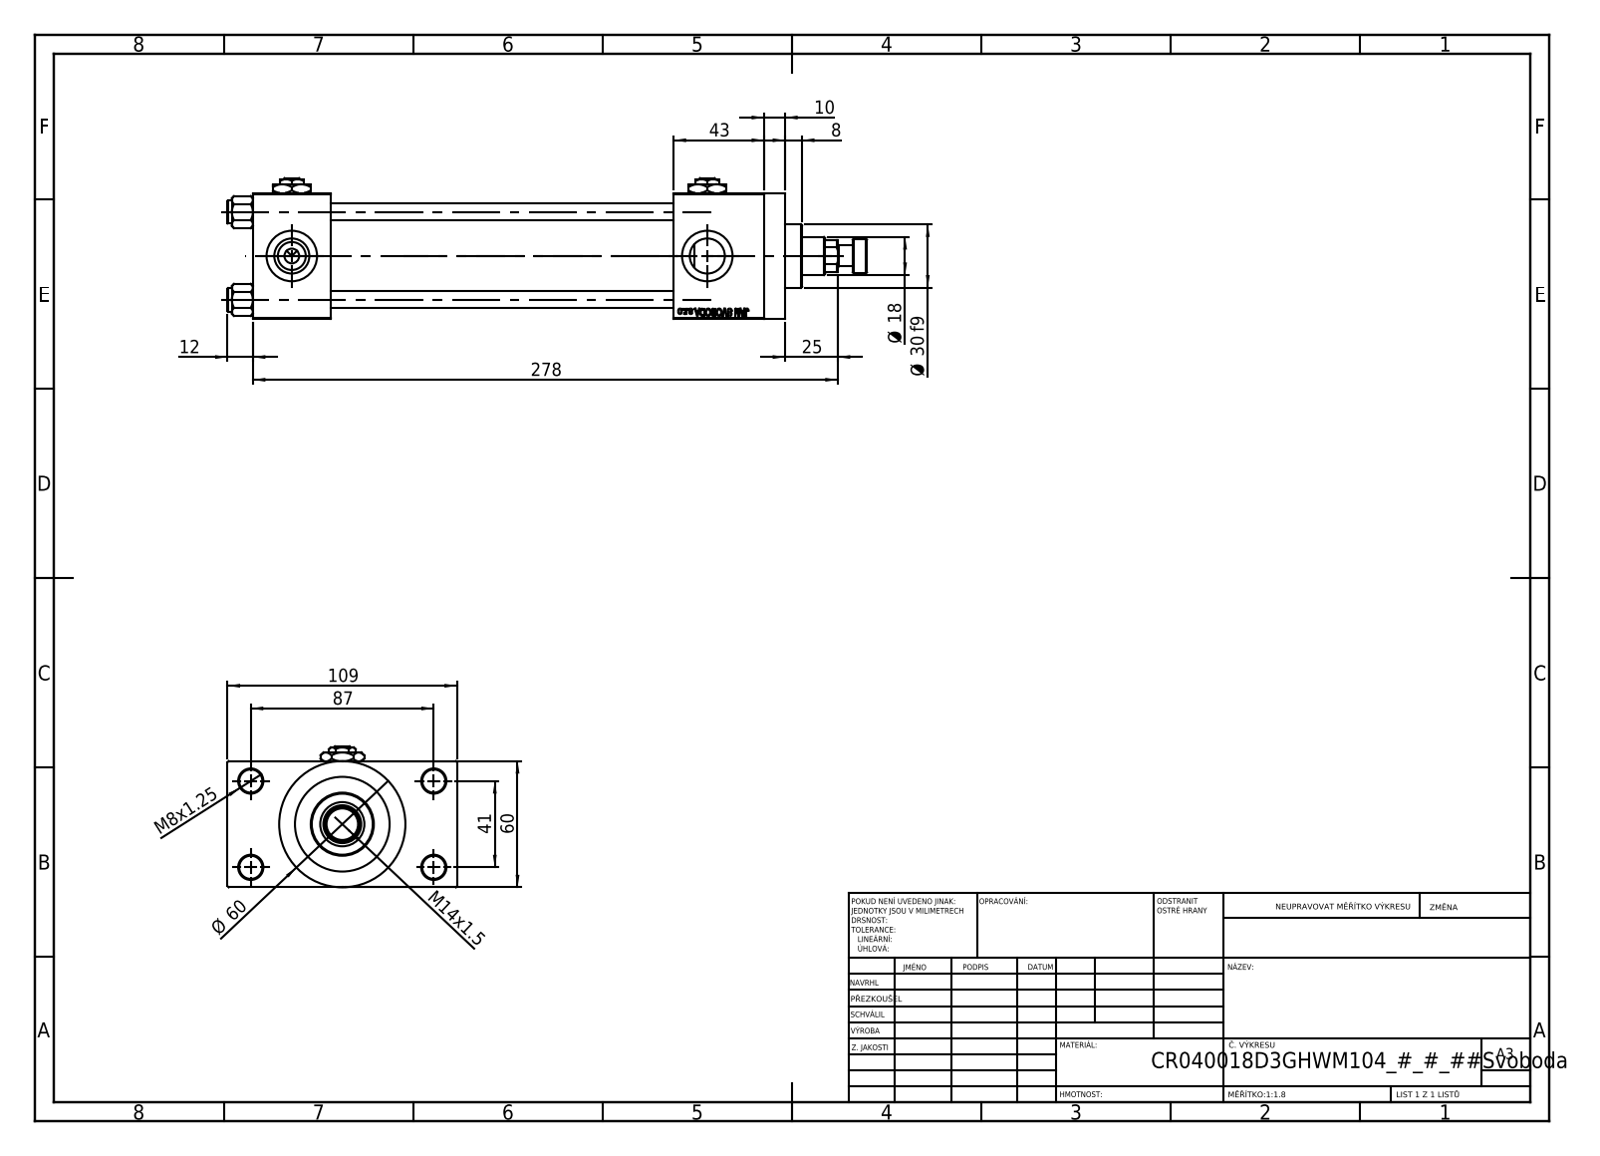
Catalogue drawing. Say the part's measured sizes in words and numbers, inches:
The part is named "V215_VC_A; V215CR_ROD_END_W; NUT_M5_D; V215CR_D_Body (+3 more)". Its 3-D file was written by "SolidWorks 2019 (CONFIG_CONTROL_DESIGN)". It is 14 solids with 1218 faces: 549 planar, 103 cylindrical and 566 other. Overall it measures 11.969 by 4.291 by 2.638 inches. Its volume is 36.78 cubic inches and its surface area 265.1 square inches. Round holes: 4 of diameter 0.315, 4 of diameter 0.433, 4 of diameter 0.656, 4 of diameter 0.945, 3 of diameter 0.276, 1 of diameter 0.335, 1 of diameter 0.709, 1 of diameter 0.827, 1 of diameter 1.22, 1 of diameter 1.575, 1 of diameter 1.772. Round bosses or shafts: 4 of diameter 0.433, 1 of diameter 2.362, 1 of diameter 1.811, 1 of diameter 1.181, 1 of diameter 0.63, 1 of diameter 0.394. Partial cylindrical surfaces (rounded edges, fillets, slot ends): 1 of radius 0.335. The main face-to-face distances are 2.362, 0.965, 6.417, 3.327, 1.457, 7.874, 1.693, 9.567, 8.11, 0.394. The hole center spacings are 0.892, 1.161, 1.642, 1.856, 1.893, 2.533, 3.011, 1.614.
